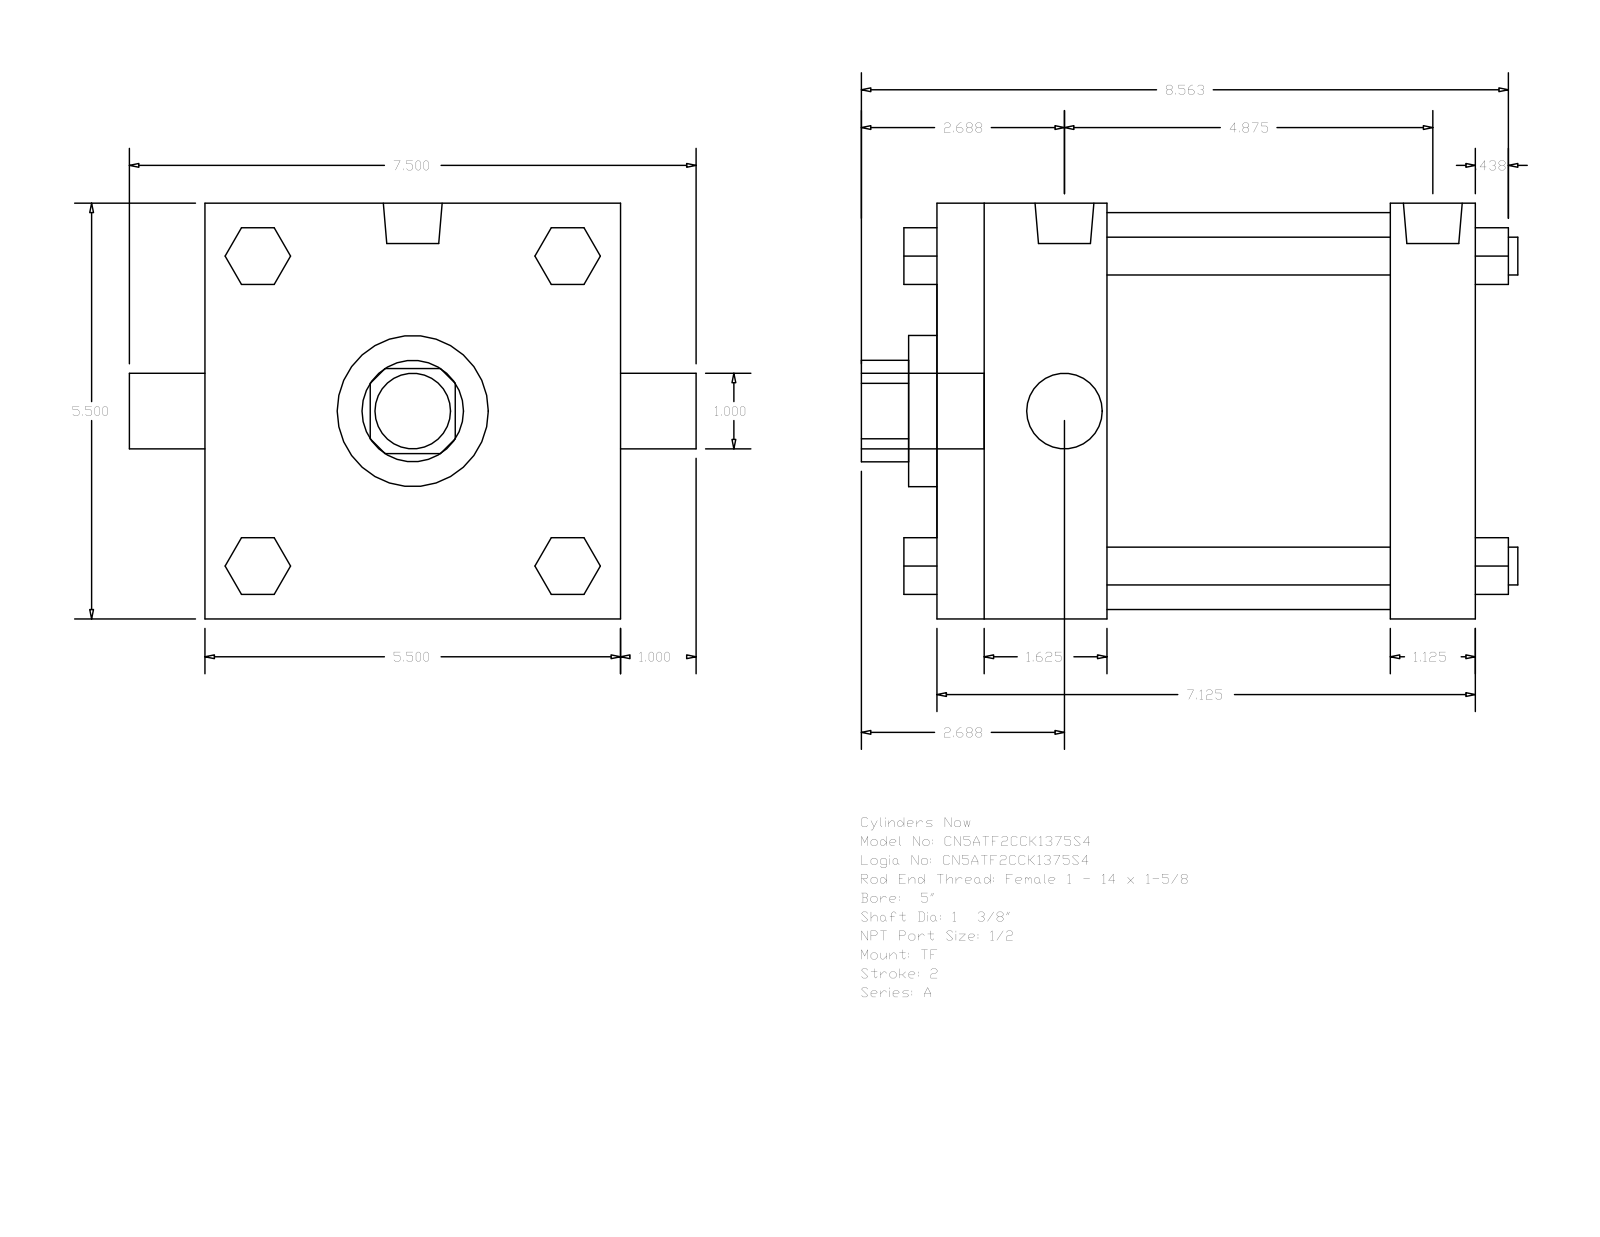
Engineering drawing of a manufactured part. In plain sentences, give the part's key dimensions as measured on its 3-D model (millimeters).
The part is named "A_TF__0500_1.375". Its 3-D file was written by "GSSL Pune (CONFIG_CONTROL_DESIGN)". It is 0 solids with 120 faces: 92 planar, 28 cylindrical and 0 other. Overall it measures 220.66 by 190.5 by 139.7 millimeters. Round holes: 1 of diameter 25.4, 1 of diameter 34.92, 1 of diameter 50.8, 1 of diameter 133.35. Round bosses or shafts: 4 of diameter 12.7, 3 of diameter 8.73, 2 of diameter 19.77, 1 of diameter 25.4. Partial cylindrical surfaces (rounded edges, fillets, slot ends): 1 of radius 17.06. The main face-to-face distances are 139.7, 180.98, 28.58, 152.4, 57.15, 95.25, 123.83, 19.05, 52.07, 90.18.
